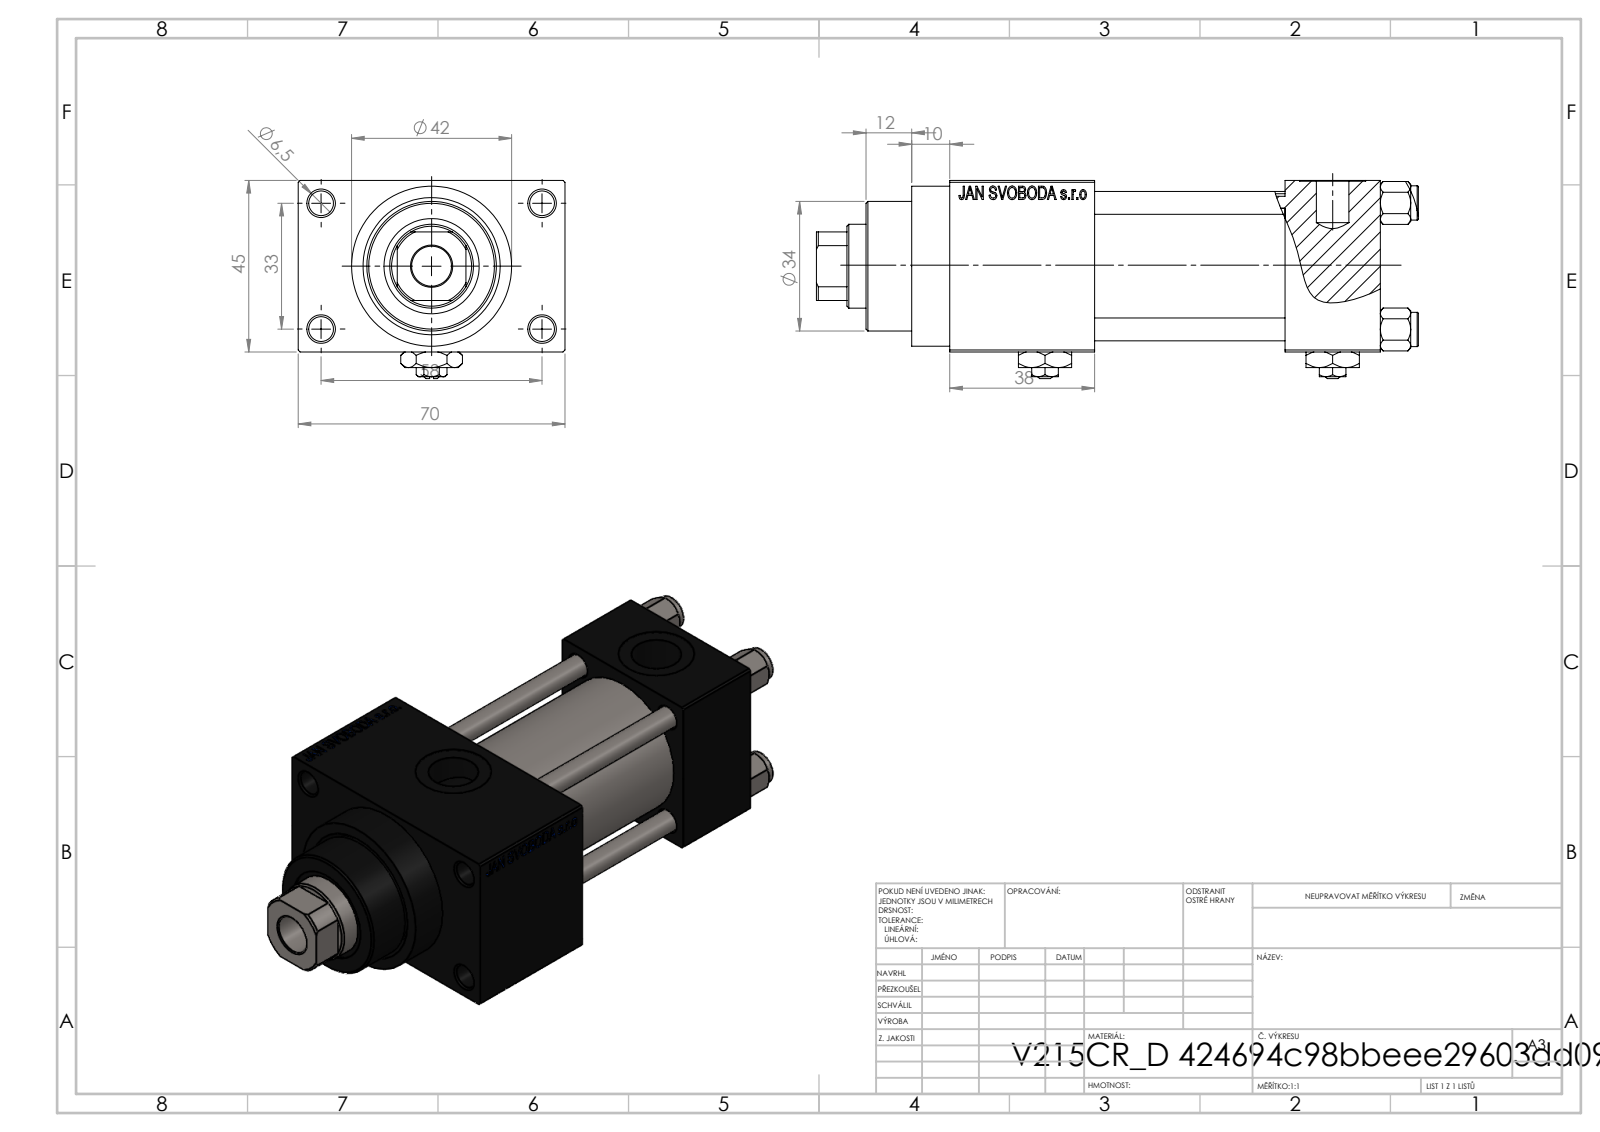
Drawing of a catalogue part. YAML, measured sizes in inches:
part_name: "V215CR_D_Body; V215_VC_A; NUT_M5_D; V215CR_VCP_D (+2 more)"
step_written_by: "SolidWorks 2019 (CONFIG_CONTROL_DESIGN)"
units: inches
bodies: {solids: 13, faces: 1204, planar: 542, cylindrical: 100, other: 562}
overall_size: [6.22, 2.756, 2.047]
volume: 14.84
surface_area: 125.7
round_holes:
  - {diameter: 0.236, count: 4}
  - {diameter: 0.256, count: 4}
  - {diameter: 0.276, count: 2}
  - {diameter: 0.518, count: 2}
  - {diameter: 0.787, count: 2}
  - {diameter: 0.413, count: 1}
  - {diameter: 0.866, count: 1}
  - {diameter: 0.945, count: 1}
  - {diameter: 0.984, count: 1}
  - {diameter: 1.26, count: 1}
  - {diameter: 1.299, count: 1}
round_bosses_or_shafts:
  - {diameter: 0.354, count: 4}
  - {diameter: 1.654, count: 1}
  - {diameter: 1.496, count: 1}
  - {diameter: 1.339, count: 1}
partial_cylinders:
  - {radius: 0.413, count: 1}
face_to_face_distances: [1.772, 0.984, 0.492, 2.264, 1.969, 2.953, 3.465, 2.756, 1.496, 4.449]
hole_center_spacings: [0.488, 0.924, 1.307, 1.314, 1.392, 1.795, 2.219, 1.299]
